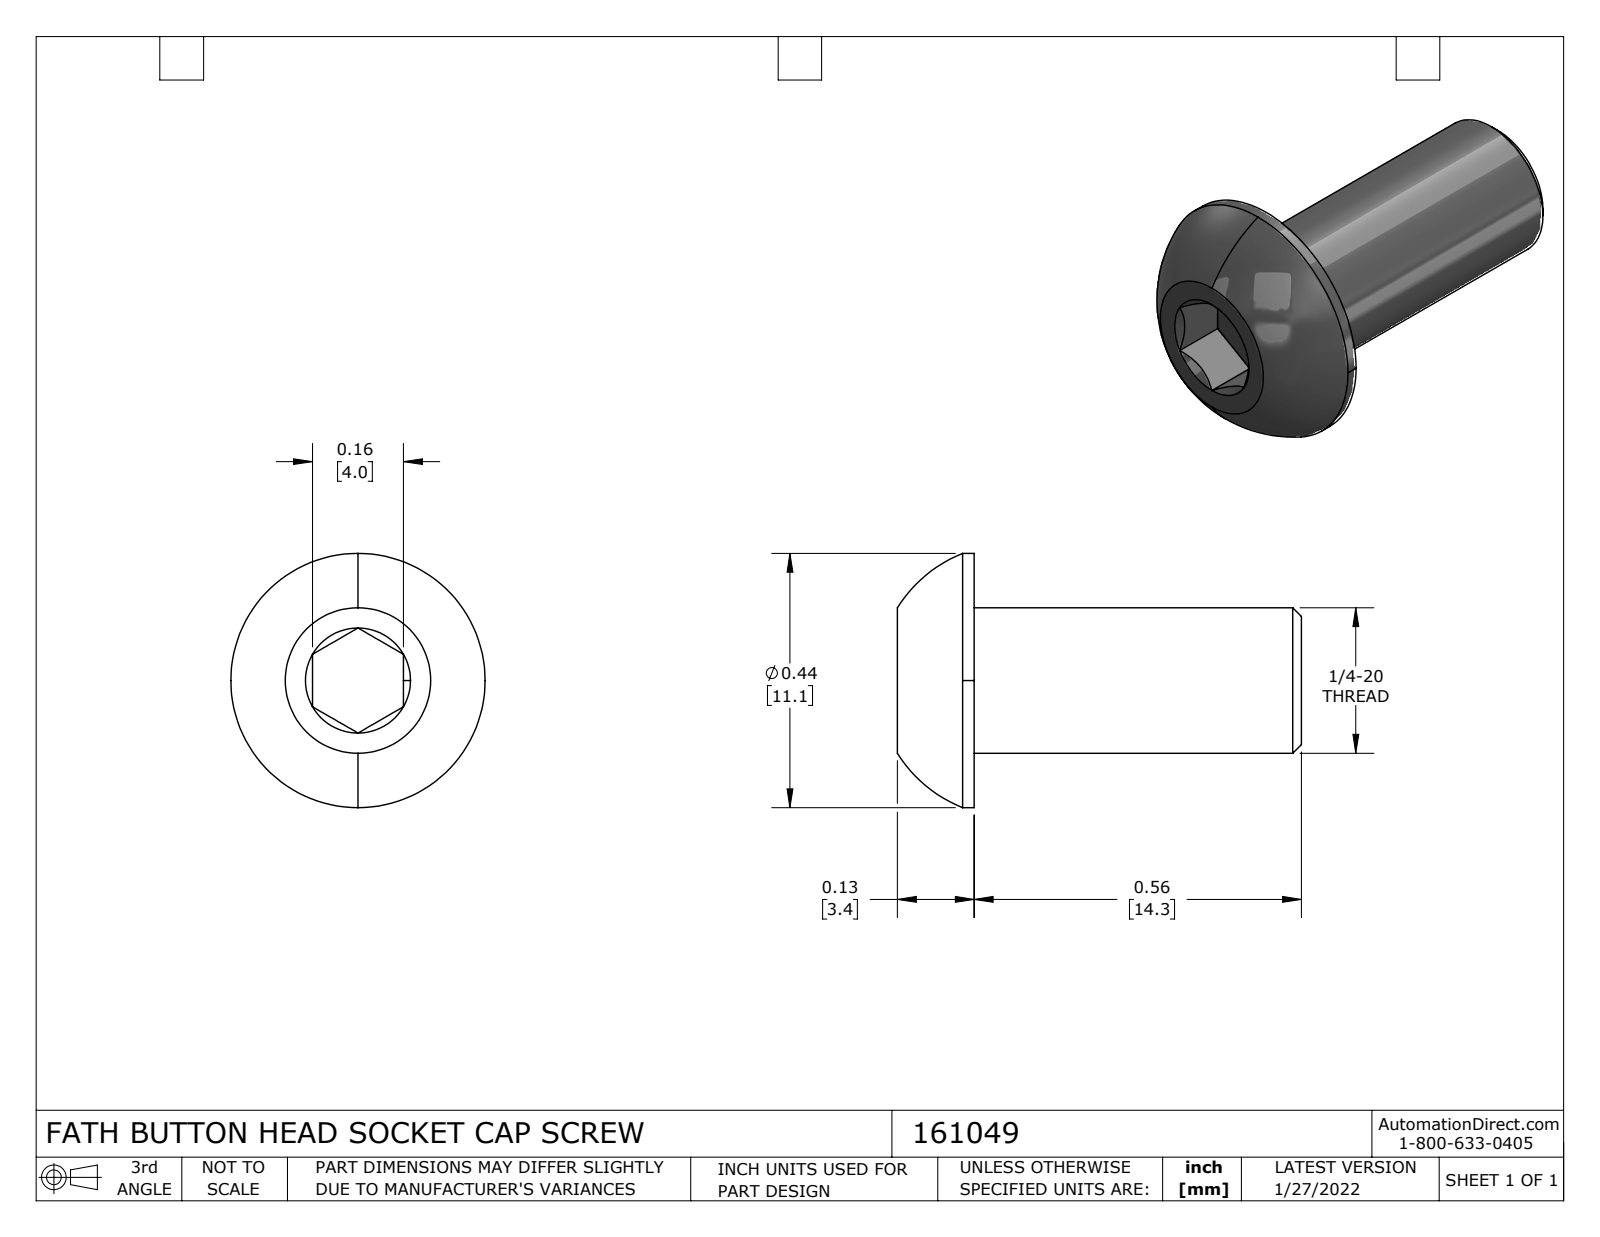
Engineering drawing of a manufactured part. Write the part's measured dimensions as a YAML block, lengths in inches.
part_name: "161049"
step_written_by: "SolidWorks 2021 (CONFIG_CONTROL_DESIGN)"
units: inches
bodies: {solids: 1, faces: 29, planar: 12, cylindrical: 4, other: 13}
overall_size: [0.694, 0.437, 0.437]
volume: 0.04
surface_area: 0.88
round_bosses_or_shafts:
  - {diameter: 0.437, count: 1}
  - {diameter: 0.25, count: 1}
face_to_face_distances: [0.563, 0.694, 0.132, 0.602, 0.039, 0.093, 0.156]
